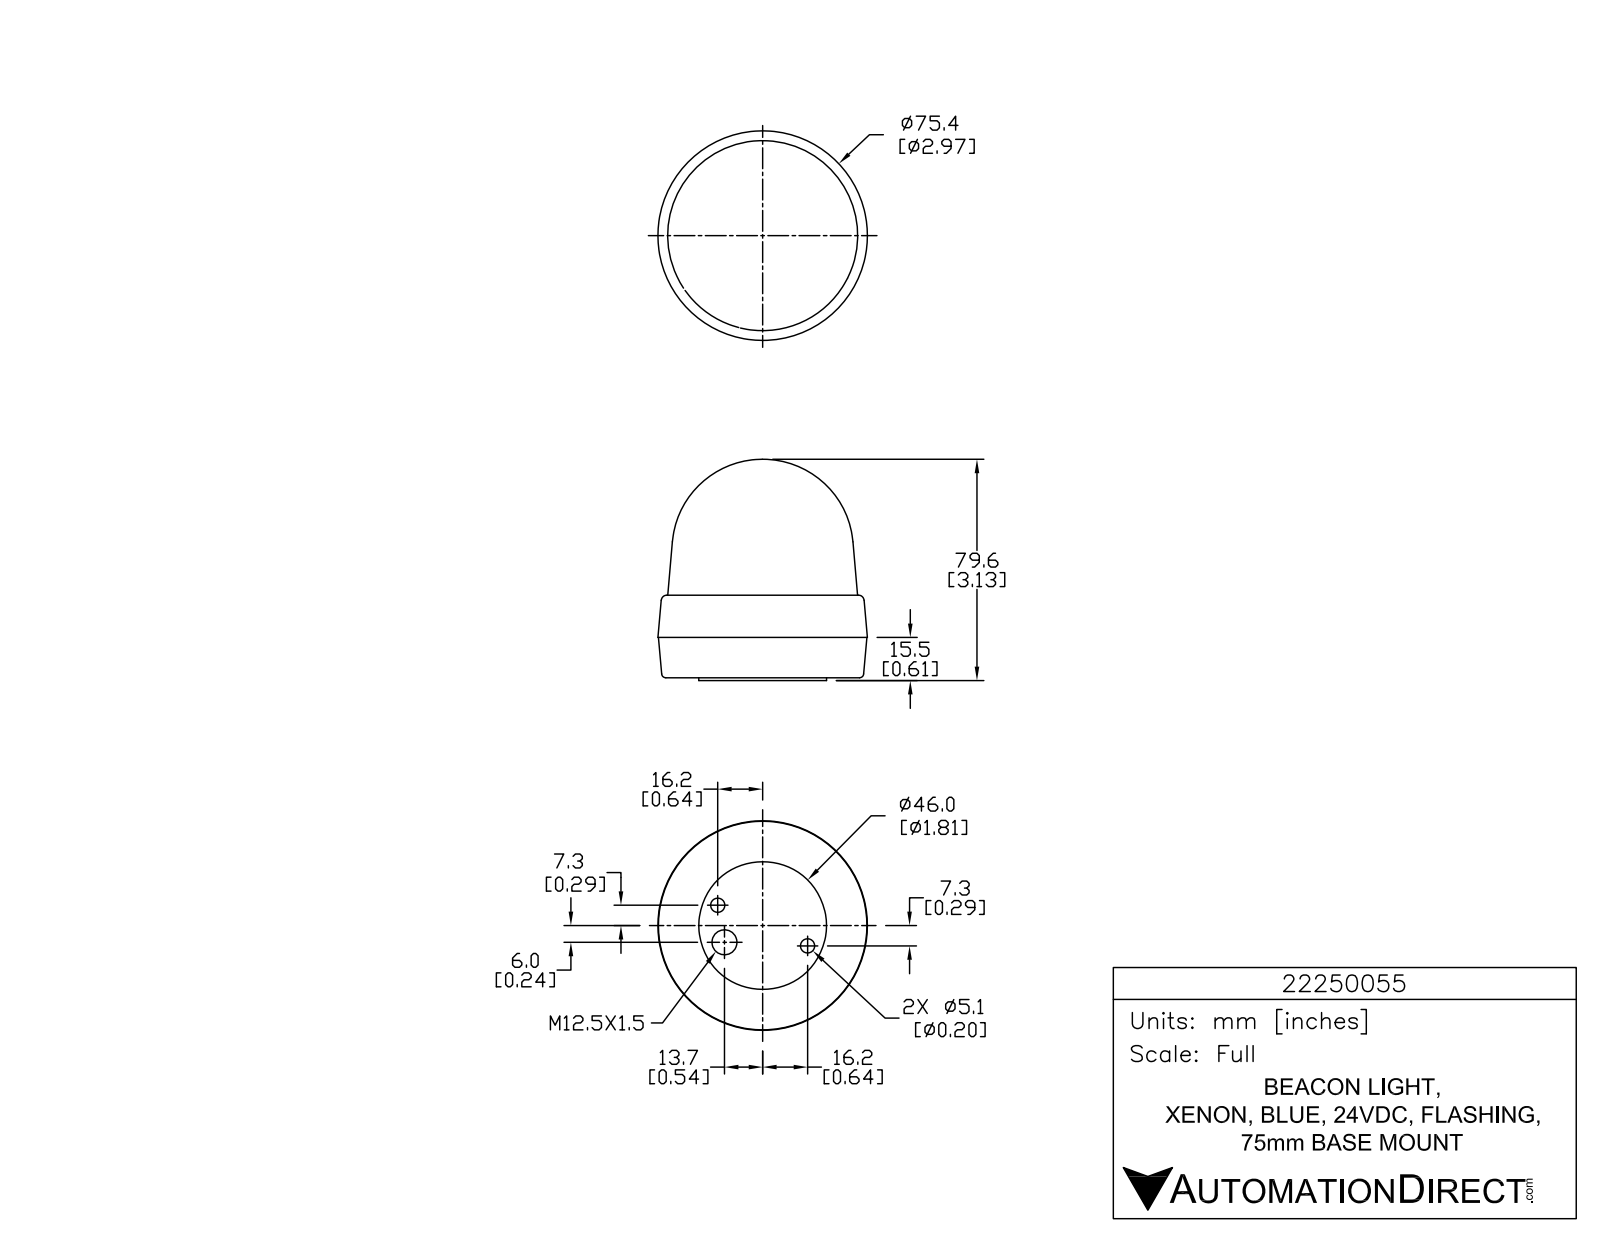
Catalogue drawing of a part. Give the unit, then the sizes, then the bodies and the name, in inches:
Units: inches
Overall size (bounding box): 3.133 × 2.967 × 2.967
Round holes (diameter × count): ⌀0.059 ×3, ⌀0.201 ×2, ⌀0.354 ×1
Round bosses / shafts (diameter × count): ⌀0.339 ×3, ⌀0.084 ×3, ⌀1.811 ×1
Partial cylindrical surfaces — rounded edges, fillets, slot ends (radius × count): R0.005 ×9, R0.005 ×6, R0.012 ×6, R0.012 ×6, R0.012 ×6, R0.196 ×6, R0.005 ×3, R0.005 ×3
Main face-to-face distances: 0.039, 1.209, 1.17, 0.61, 0.571, 0.599, 1.566, 1.527, 0.956, 0.357
Hole centre spacings: 0.534, 1.179, 1.398
Volume: 15.79 in³ · Surface area: 33.7 in²
Bodies: 1 solid, 773 faces (526 planar, 163 cylindrical, 84 other)
Part name (STEP PRODUCT): 22250055
STEP written by: SolidWorks 2015 (AUTOMOTIVE_DESIGN)
